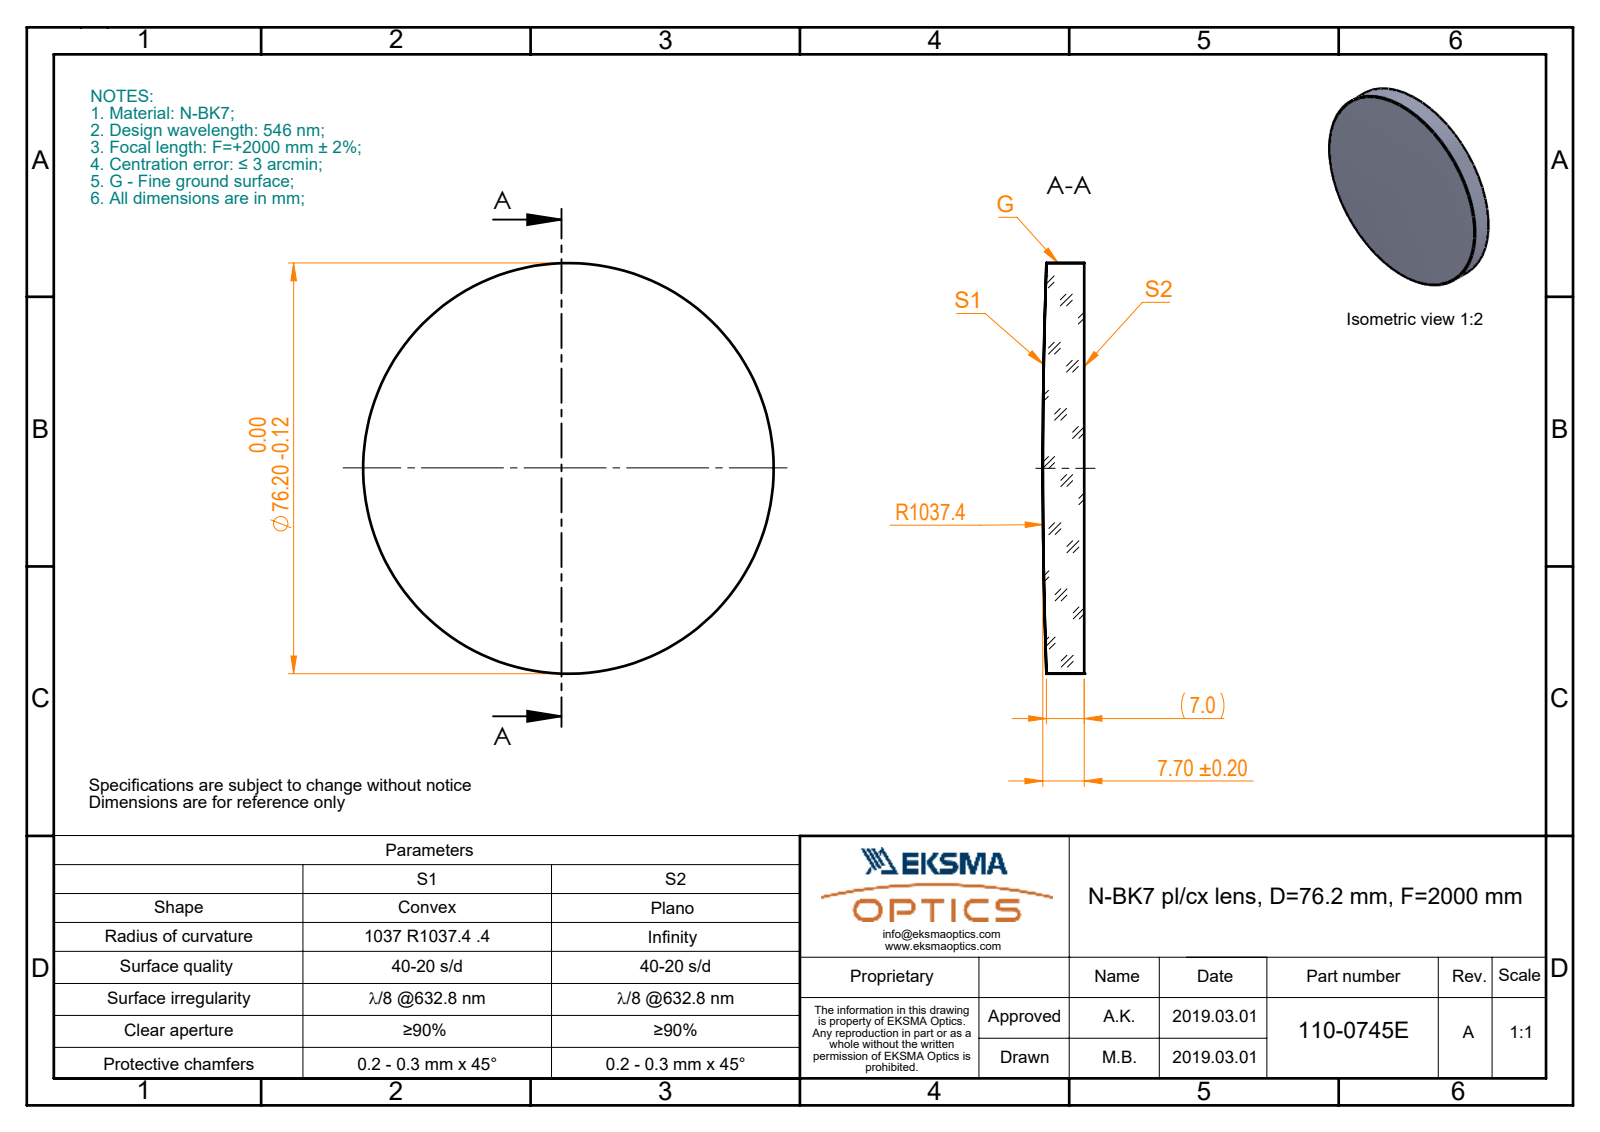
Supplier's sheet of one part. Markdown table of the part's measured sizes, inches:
| quantity | value |
| --- | --- |
| part name | 110-0745E BK7 pl-cx 76.2 F2000 |
| STEP written by | SolidWorks 2017 (CONFIG_CONTROL_DESIGN) |
| units | inches |
| bodies | 1 solid, 5 faces (1 planar, 2 cylindrical, 2 other) |
| overall size | 3 × 3 × 0.303 |
| volume | 2.045 in³ |
| surface area | 16.74 in² |
| round bosses / shafts (diameter × count) | 3 × 1 |
